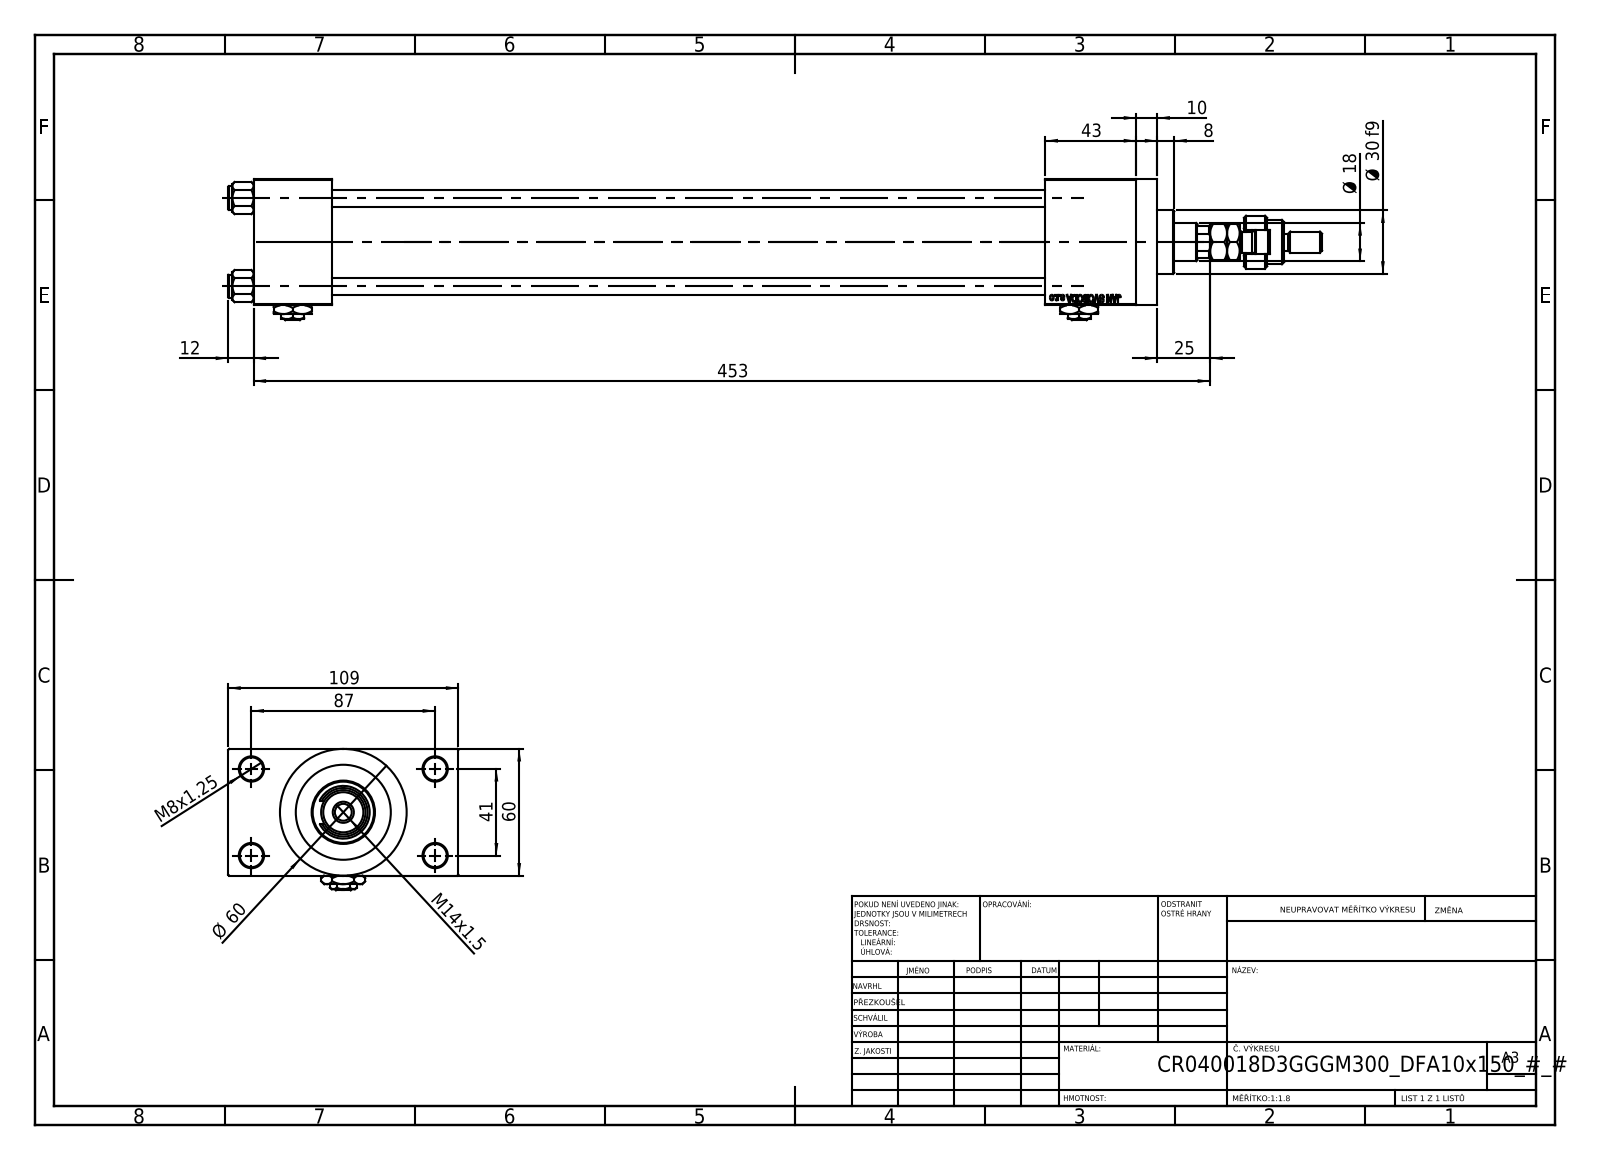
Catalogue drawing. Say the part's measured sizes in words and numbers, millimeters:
The part is named "Zatka_pro_OIL_PORT; V215_VC_A; V215CR_D_Body; FEMALE_PART_FOR_DFA (+4 more)". Its 3-D file was written by "SolidWorks 2019 (CONFIG_CONTROL_DESIGN)". It is 15 solids with 1291 faces: 574 planar, 113 cylindrical and 604 other. Overall it measures 518 by 109 by 67 millimeters. Its volume is 768 409 cubic millimeters and its surface area 248 992 square millimeters. Round holes: 4 of diameter 8, 4 of diameter 11, 2 of diameter 7, 2 of diameter 16.66, 2 of diameter 24, 1 of diameter 8.5, 1 of diameter 18, 1 of diameter 21, 1 of diameter 31, 1 of diameter 40, 1 of diameter 45. Round bosses or shafts: 4 of diameter 11, 1 of diameter 60, 1 of diameter 46, 1 of diameter 30, 1 of diameter 25, 1 of diameter 16, 1 of diameter 10, 1 of diameter 8. Partial cylindrical surfaces (rounded edges, fillets, slot ends): 1 of radius 5.5, 1 of radius 8.5, 1 of radius 8.75. The main face-to-face distances are 60, 24.5, 84.5, 338, 37, 375, 43, 418, 381, 109. The hole center spacings are 22.65, 29.49, 41.7, 47.15, 48.09, 64.35, 76.49, 41.
